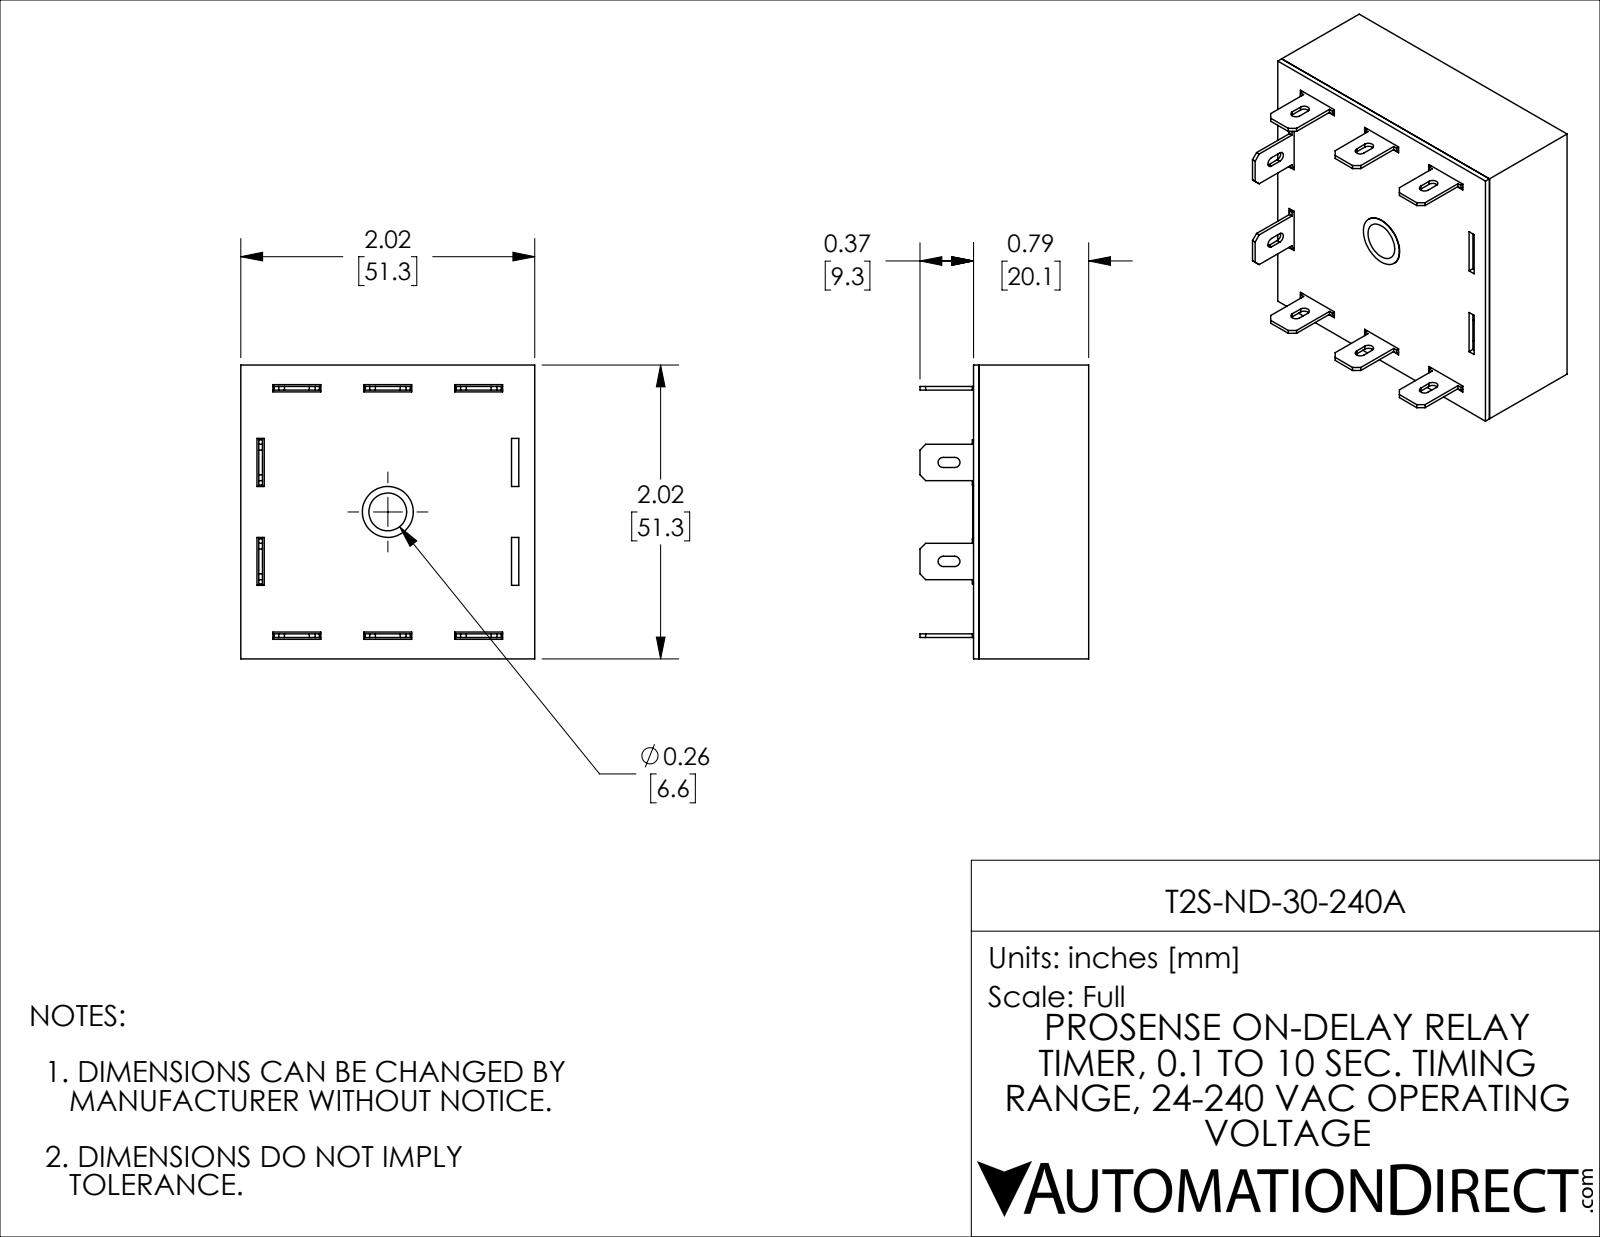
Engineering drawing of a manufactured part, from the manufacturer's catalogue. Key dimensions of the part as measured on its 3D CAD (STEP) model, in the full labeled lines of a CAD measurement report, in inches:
Part name (STEP PRODUCT): T2S-ND-30-240A
STEP written by: SolidWorks 2021 (CONFIG_CONTROL_DESIGN)
Units: inches
Bodies: 10 solids, 256 faces (234 planar, 20 cylindrical, 2 other)
Overall size (bounding box): 2.02 × 2.02 × 1.16
Volume: 0.674 in³ · Surface area: 35.37 in²
Round holes (diameter × count): ⌀0.35 ×1
Partial cylindrical surfaces — rounded edges, fillets, slot ends (radius × count): R0.035 ×10
Main face-to-face distances: 0.045, 1.975, 0.754, 0.792, 0.038, 0.709, 0.747, 2.02, 1.93, 0.147
